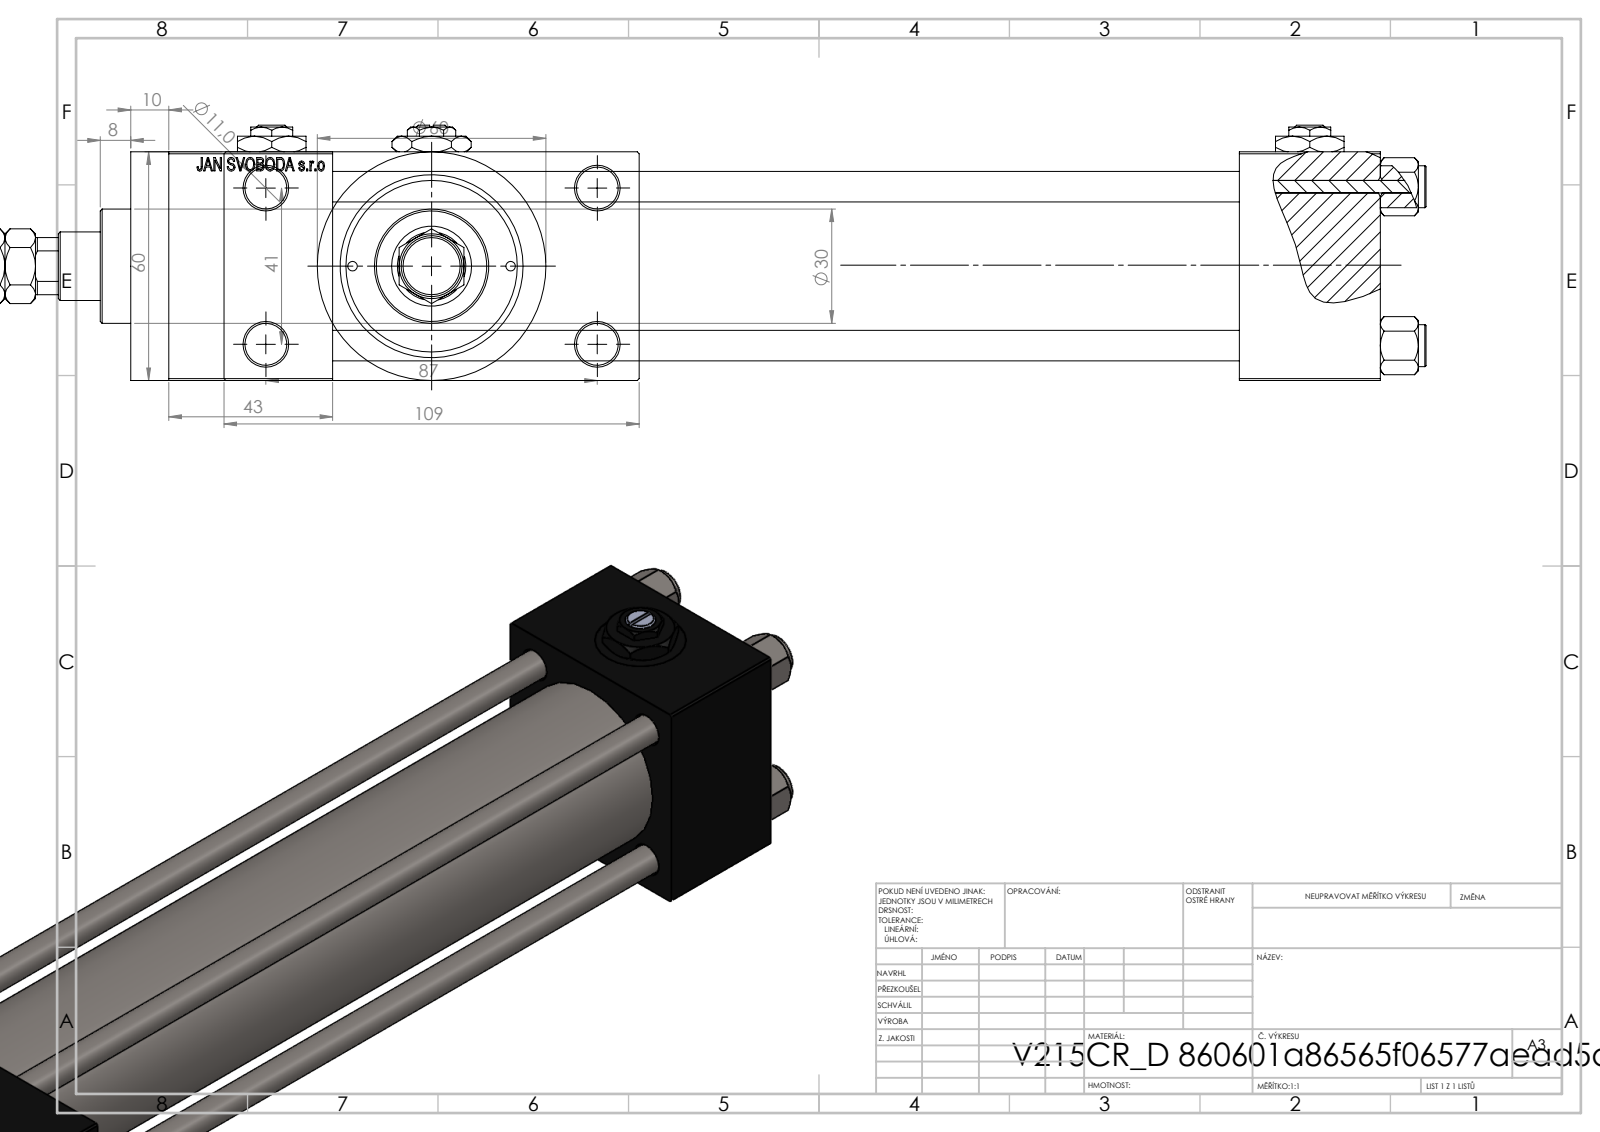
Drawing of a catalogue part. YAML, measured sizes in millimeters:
part_name: "V215CR_D_TYCINKA; V215CR_D_Body; V215_VC_A; Zatka_pro_OIL_PORT (+3 more)"
step_written_by: "SolidWorks 2019 (CONFIG_CONTROL_DESIGN)"
units: millimeters
bodies: {solids: 14, faces: 1265, planar: 564, cylindrical: 107, other: 594}
overall_size: [393, 109, 67]
volume: 670495
surface_area: 204120
round_holes:
  - {diameter: 8, count: 4}
  - {diameter: 11, count: 4}
  - {diameter: 16.66, count: 4}
  - {diameter: 24, count: 4}
  - {diameter: 7, count: 3}
  - {diameter: 2.5, count: 2}
  - {diameter: 8.5, count: 1}
  - {diameter: 18, count: 1}
  - {diameter: 21, count: 1}
  - {diameter: 31, count: 1}
  - {diameter: 40, count: 1}
  - {diameter: 45, count: 1}
round_bosses_or_shafts:
  - {diameter: 11, count: 4}
  - {diameter: 60, count: 1}
  - {diameter: 46, count: 1}
  - {diameter: 30, count: 1}
  - {diameter: 16, count: 1}
  - {diameter: 10, count: 1}
partial_cylinders:
  - {radius: 8.5, count: 1}
face_to_face_distances: [60, 238, 24.5, 84.5, 37, 275, 43, 318, 281, 53]
hole_center_spacings: [20.85, 22.65, 29.49, 30.62, 41.7, 46.53, 47.15, 48.09]
